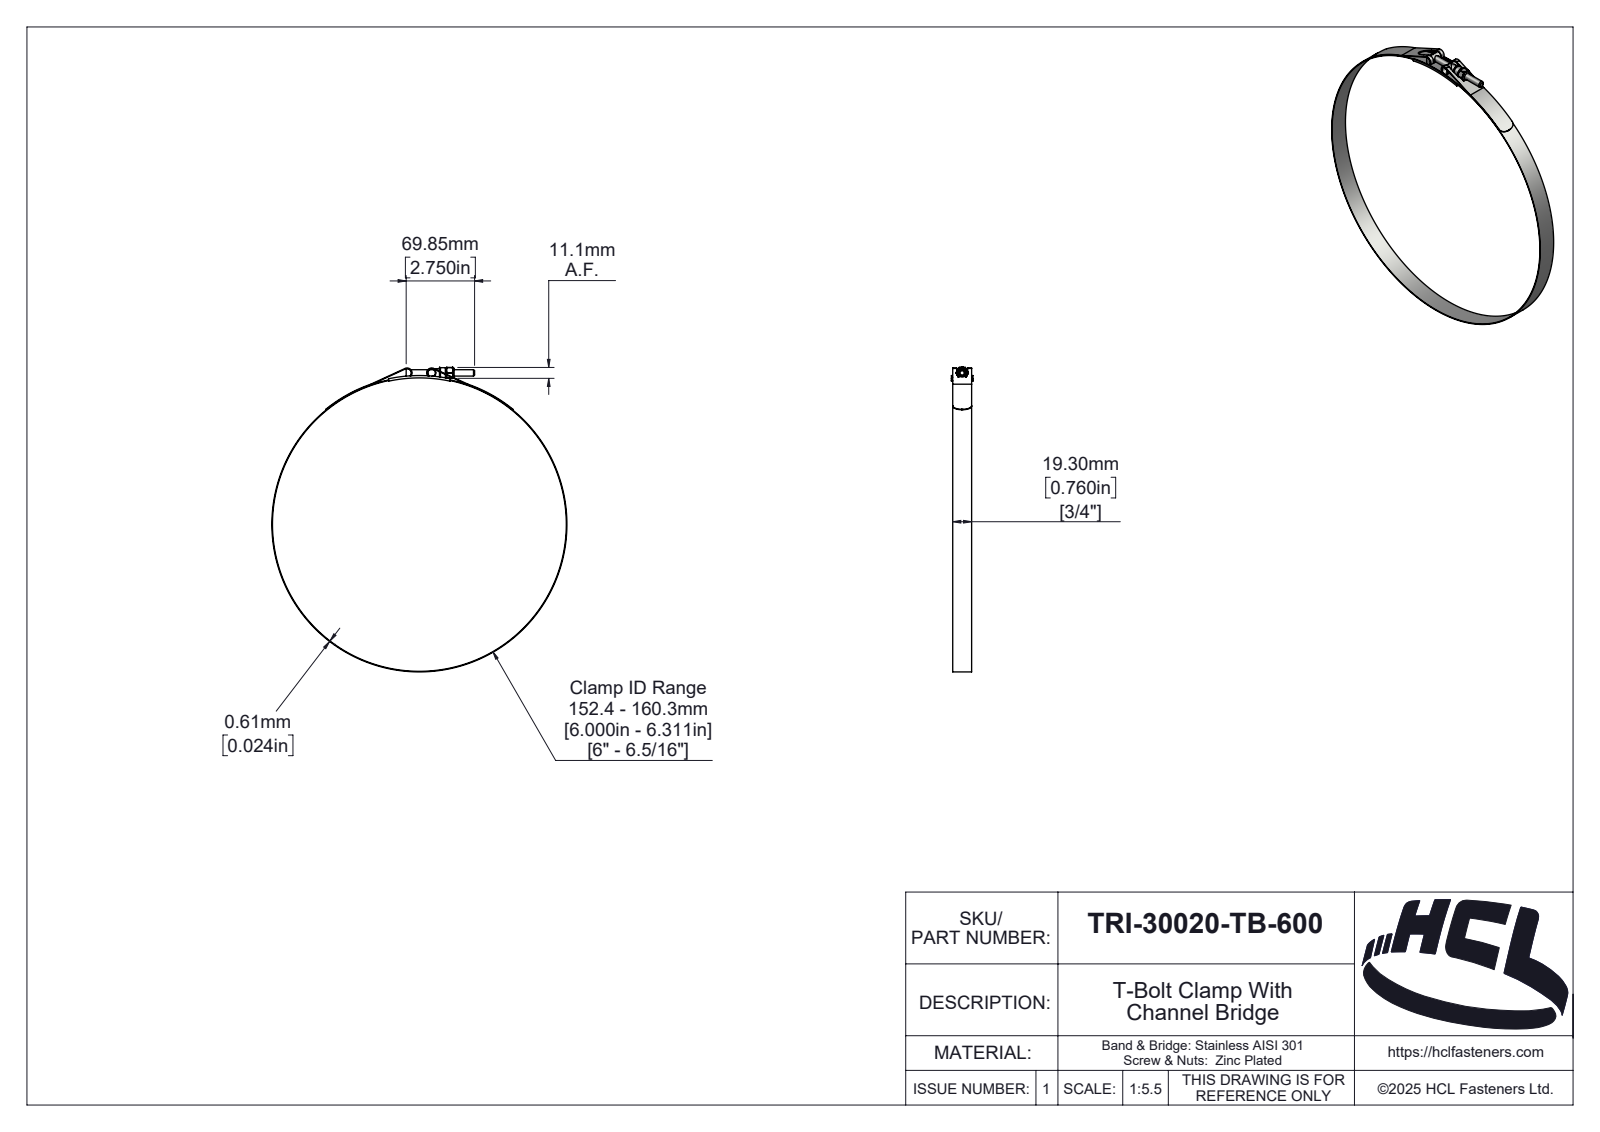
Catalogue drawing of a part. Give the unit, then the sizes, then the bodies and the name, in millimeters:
Units: millimetres
Overall size (bounding box): 310.83 × 301.22 × 22
Round holes (diameter × count): ⌀5.4 ×1, ⌀6.35 ×1, ⌀6.5 ×1, ⌀7.58 ×1, ⌀300 ×1
Round bosses / shafts (diameter × count): ⌀8.58 ×2, ⌀301.22 ×1, ⌀10.58 ×1
Partial cylindrical surfaces — rounded edges, fillets, slot ends (radius × count): R0.39 ×6, R0.5 ×2, R4.39 ×2, R5 ×2, R0.59 ×1, R2.42 ×1, R3.03 ×1, R3.19 ×1
Main face-to-face distances: 0.61, 19.3, 1.35, 20.65, 0.74, 21.39, 20.04, 22, 20.78, 11.11
Hole centre spacings: 155
Volume: 18 073 mm³ · Surface area: 51 486 mm²
Bodies: 6 solids, 330 faces (44 planar, 122 cylindrical, 164 other)
Part name (STEP PRODUCT): TRI-30020-TB-600
STEP written by: SolidWorks 2025 (AUTOMOTIVE_DESIGN)
